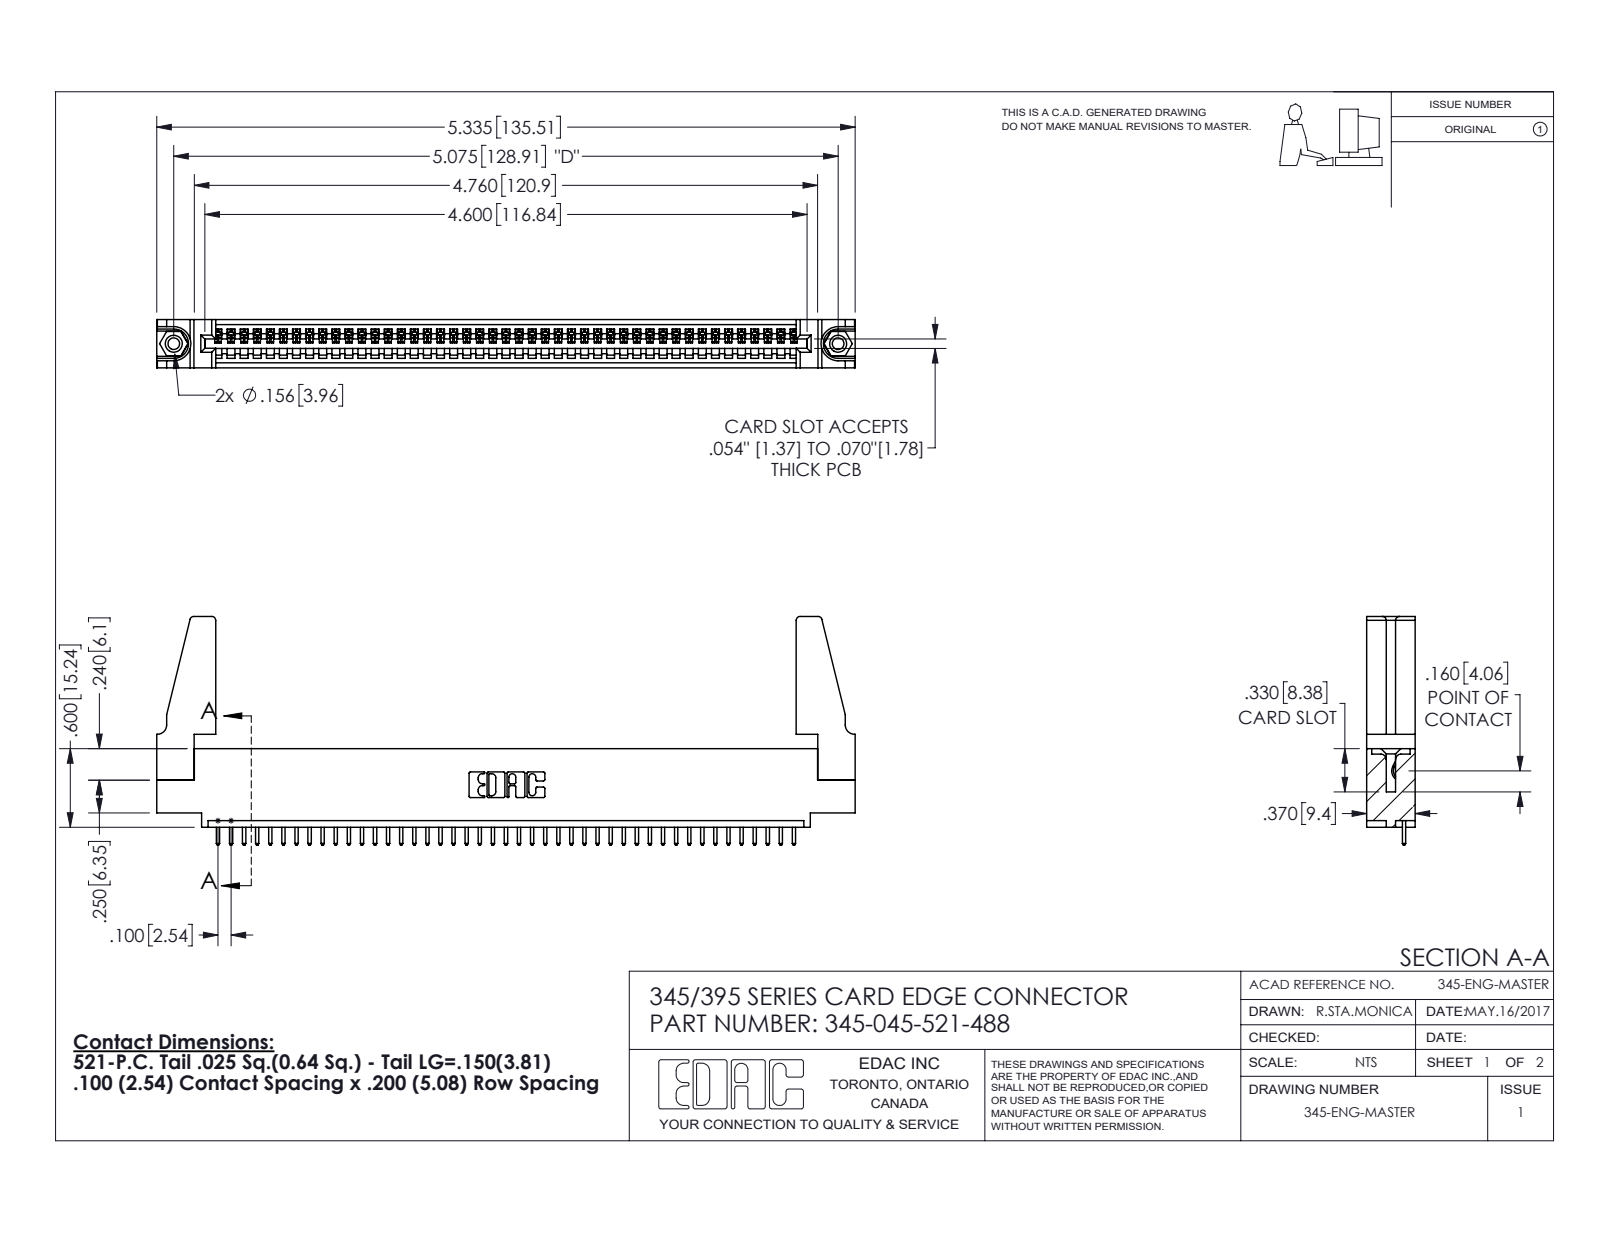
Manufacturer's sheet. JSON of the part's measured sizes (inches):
{"part_name": "345 Part_0.110 Offset - 0.156 Dia-TH; 345-045-521-488; 345-292-001_345-293-121; 345-250-001_345-250-001-102 (+1 more)", "step_written_by": "SolidWorks 2016 (CONFIG_CONTROL_DESIGN)", "units": "inches", "bodies": {"solids": 50, "faces": 2864, "planar": 1956, "cylindrical": 892, "other": 16}, "overall_size": [5.336, 1.747, 0.37], "volume_in3": 0.973, "surface_area_in2": 30.42, "round_holes": [[0.089, 2], [0.125, 2], [0.156, 2], [0.064, 1]], "round_bosses_or_shafts": [[0.155, 2]], "partial_cylinders_radius": [[0.006, 90], [0.01, 90], [0.01, 22], [0.03, 8], [0.007, 6], [0.031, 6], [0.026, 3], [0.031, 2]], "face_to_face_distances": [0.072, 0.298, 0.37, 0.2, 0.098, 0.272, 0.025, 0.225, 0.149, 0.072], "hole_center_spacings": [0.27, 4.839, 5.075]}
